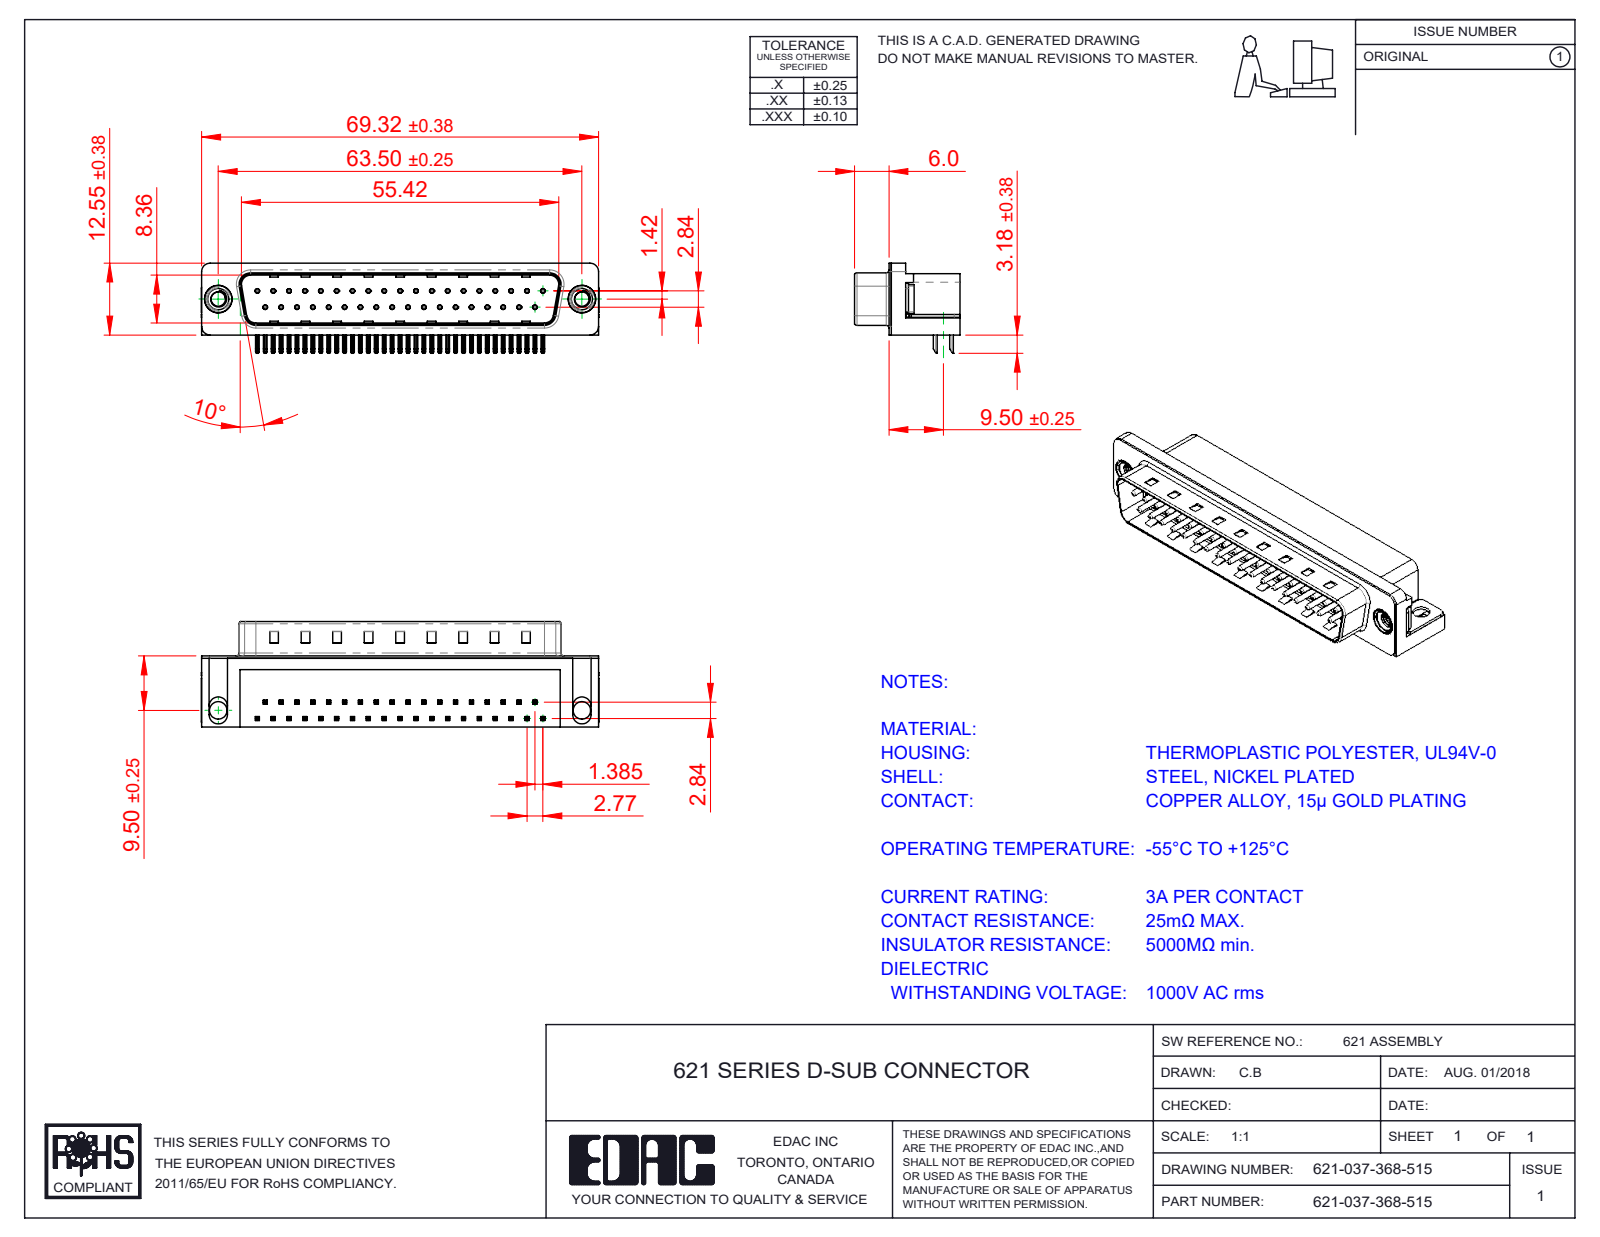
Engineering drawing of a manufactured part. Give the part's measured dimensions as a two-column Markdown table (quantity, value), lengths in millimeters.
| quantity | value |
| --- | --- |
| part name | 621 Contact Top; 621 Housing_37 Socket; 621-037-368-515; 621 Shell_37 Socket (+3 more) |
| STEP written by | SolidWorks 2016 (CONFIG_CONTROL_DESIGN) |
| units | millimeters |
| bodies | 43 solids, 3197 faces (2011 planar, 919 cylindrical, 267 other) |
| overall size | 69.4 × 18.4 × 15.73 |
| volume | 8 614 mm³ |
| surface area | 10 085 mm² |
| round holes (diameter × count) | 0.35 × 37, 0.8 × 37, 2.5 × 2, 3.05 × 2, 4 × 2, 4.8 × 2, 5 × 2 |
| round bosses / shafts (diameter × count) | 0.75 × 37, 4.9 × 2, 4.75 × 2, 3.9 × 2 |
| partial cylindrical surfaces (radius × count) | 0.25 × 156, 0.12 × 74, 1 × 16, 0.5 × 9, 1.6 × 8, 1.5 × 7, 0.9 × 4, 2 × 4 |
| main face-to-face distances | 0.4, 12, 10.35, 8.76, 2.1, 1.7, 10.46, 10.86, 9, 12.4 |
| hole center spacings | 3.16, 2.77, 5.54, 8.31, 11.08, 13.85, 19.39, 22.16 |
